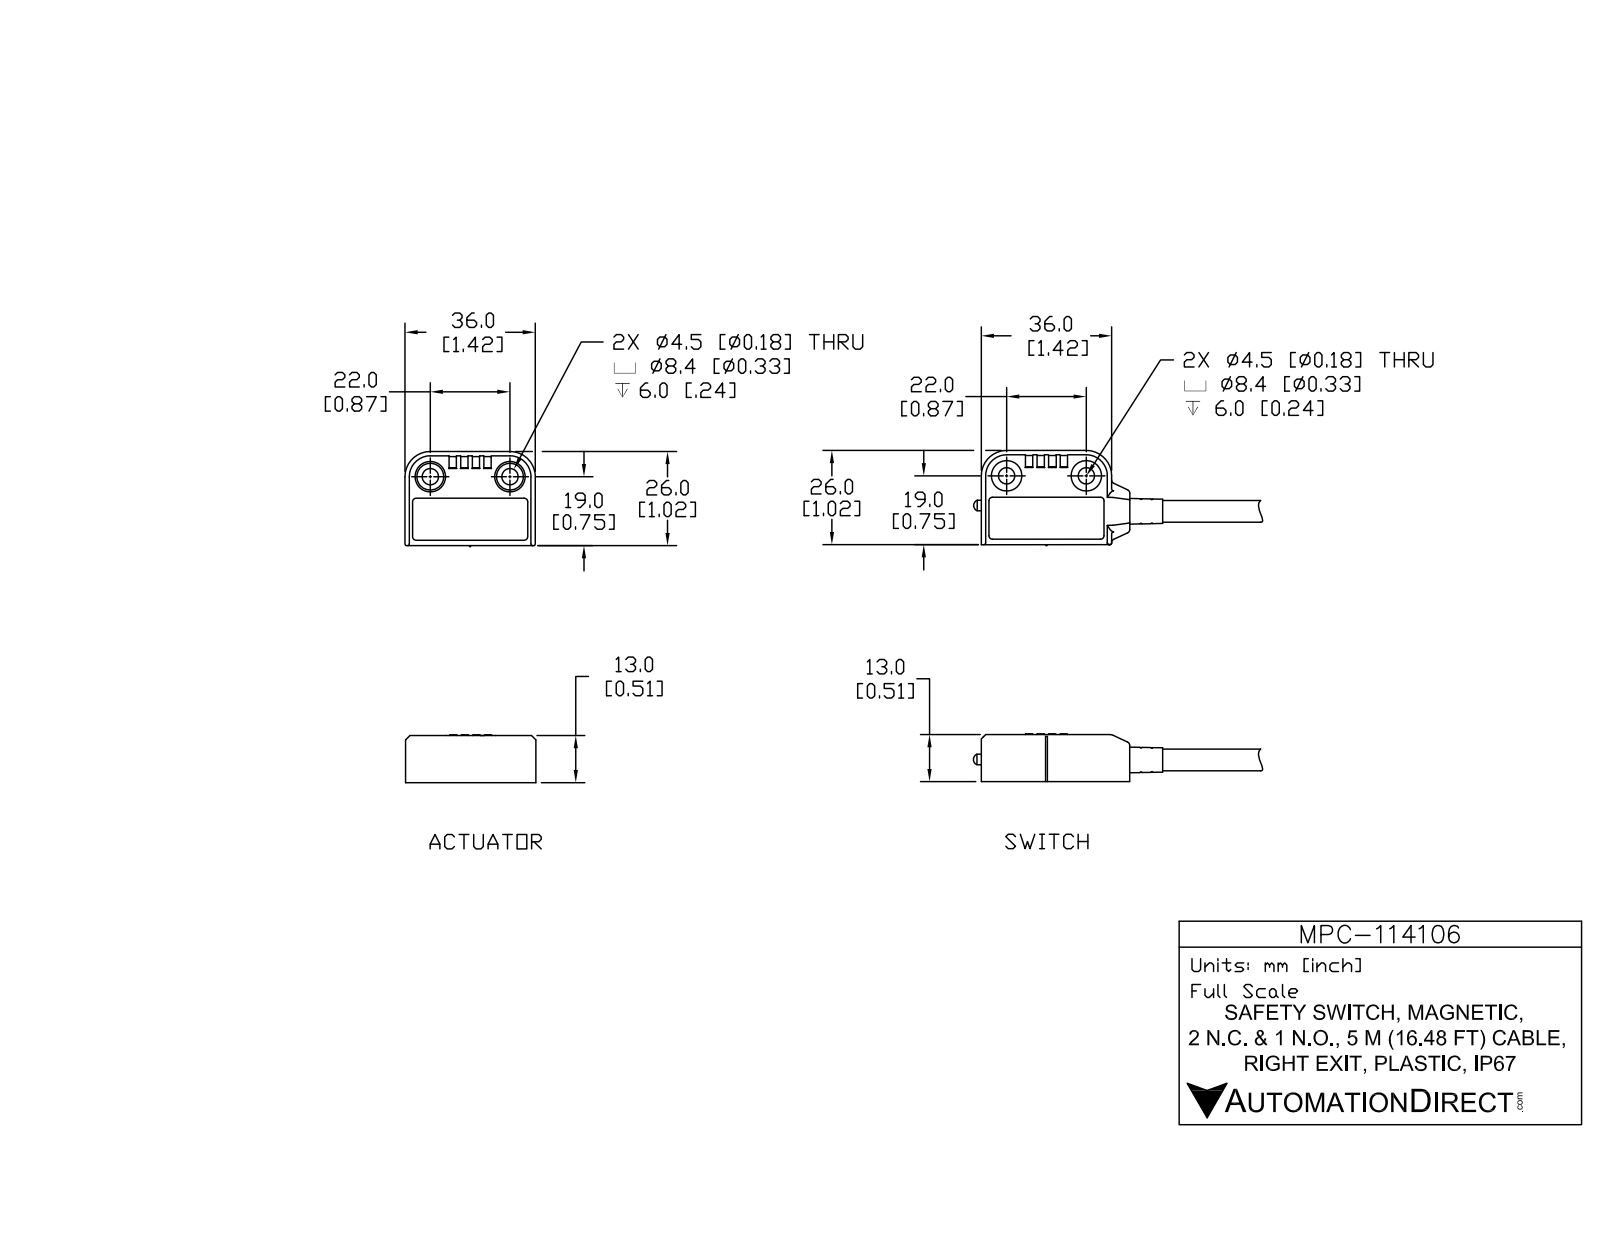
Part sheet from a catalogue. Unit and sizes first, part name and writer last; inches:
Units: inches
Overall size (bounding box): 7.748 × 2.087 × 0.528
Round holes (diameter × count): ⌀0.177 ×4, ⌀0.331 ×4, ⌀0.195 ×2, ⌀0.098 ×1, ⌀0.118 ×1, ⌀0.197 ×1, ⌀0.232 ×1, ⌀0.244 ×1, ⌀0.291 ×1
Round bosses / shafts (diameter × count): ⌀0.236 ×2, ⌀0.197 ×2, ⌀0.091 ×2, ⌀0.079 ×2, ⌀0.031 ×2, ⌀0.339 ×1, ⌀0.299 ×1, ⌀0.28 ×1
Partial cylindrical surfaces — rounded edges, fillets, slot ends (radius × count): R0.02 ×86, R0.012 ×35, R0.008 ×30, R0.004 ×17, R0.039 ×13, R0.169 ×4, R0.201 ×4, R0.276 ×4
Main face-to-face distances: 0.055, 0.508, 0.449, 0.461, 0.059, 0.047, 1.063, 0.496, 0.445, 0.031
Hole centre spacings: 0.866, 0.434, 0.445, 0.974, 1.091, 1.152, 1.393, 1.535
Volume: 1.065 in³ · Surface area: 29.74 in²
Bodies: 10 solids, 1072 faces (453 planar, 349 cylindrical, 270 other)
Part name (STEP PRODUCT): MPC-114106; MPC-114106_2; MPC-114106_1
STEP written by: SolidWorks 2017 (AUTOMOTIVE_DESIGN)
